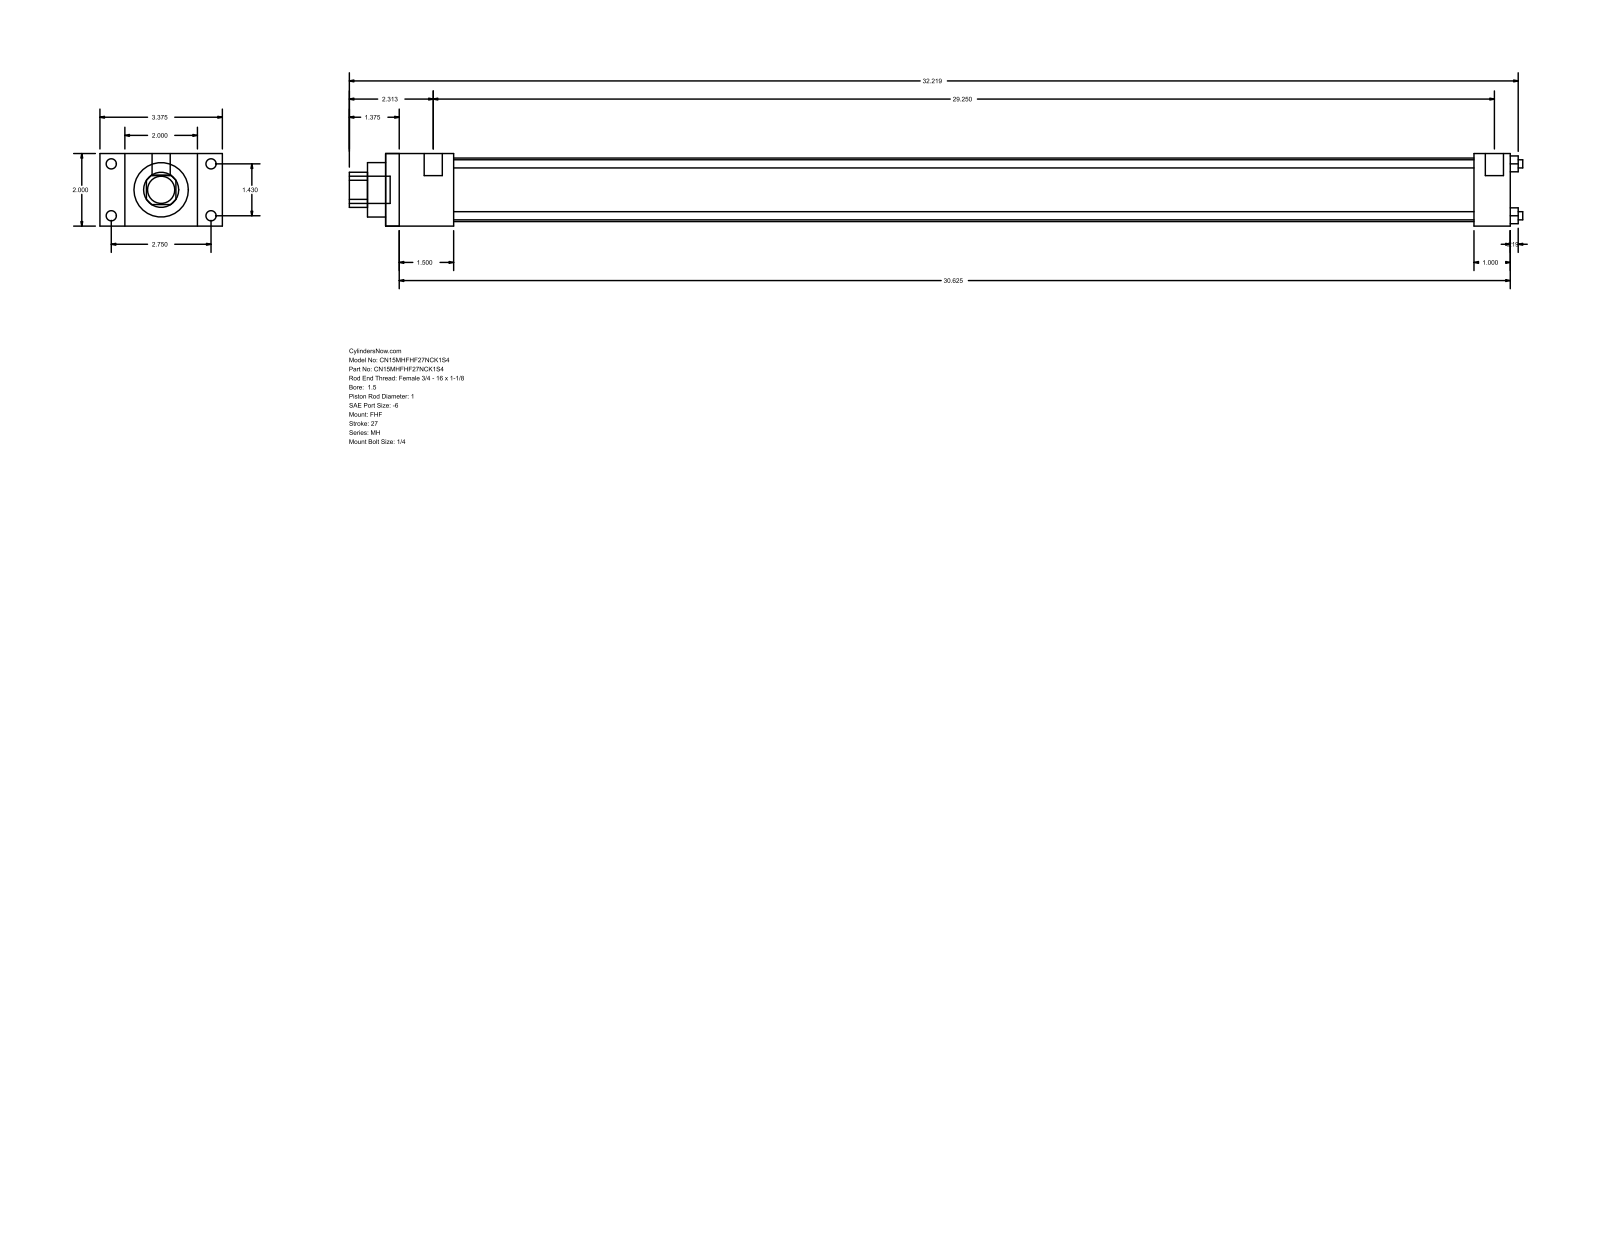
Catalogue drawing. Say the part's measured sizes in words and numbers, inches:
The part is named "MH_FHF__0150_1". Its 3-D file was written by "GSSL Pune (CONFIG_CONTROL_DESIGN)". It is 0 solids with 88 faces: 60 planar, 28 cylindrical and 0 other. Overall it measures 32.344 by 3.375 by 2 inches. Round holes: 4 of diameter 0.225, 1 of diameter 1, 1 of diameter 1.5, 1 of diameter 1.75. Round bosses or shafts: 4 of diameter 0.281, 4 of diameter 0.219, 2 of diameter 0.5, 1 of diameter 0.75. Partial cylindrical surfaces (rounded edges, fillets, slot ends): 1 of radius 0.484. The main face-to-face distances are 2, 0.687, 2.687, 1.875, 3.375, 31, 29.125, 1, 30, 28.125. The hole center spacings are 1.011, 1.43, 2.022.
